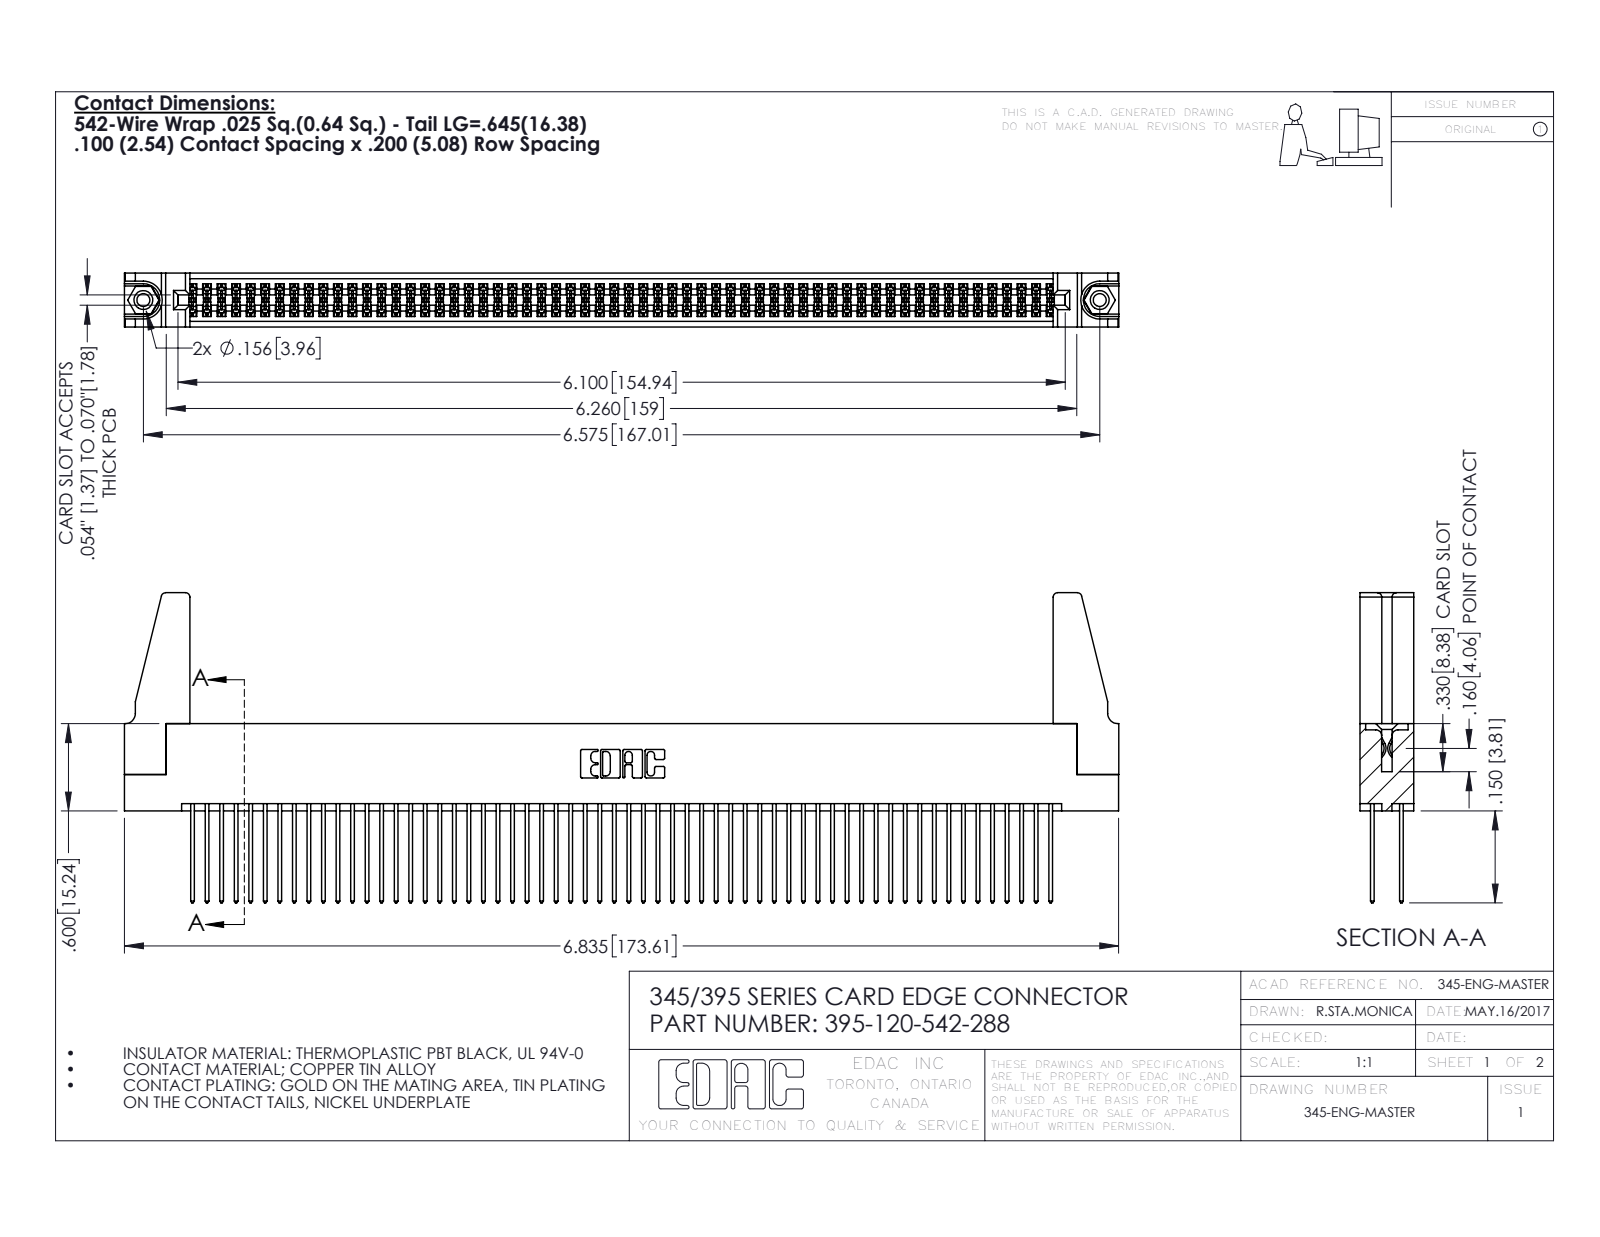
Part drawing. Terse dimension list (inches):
name: 345-292-001_345-293-142; 345 Part_Flush Mounting Lugs - 0.156 Dia-TH; 345-250-001_345-250-001-102; 345-220-078_345-220-088 (+1 more)
written by: SolidWorks 2016 (CONFIG_CONTROL_DESIGN)
unit: in
bodies: 125 solids, 6250 faces (4112 planar, 2122 cylindrical, 16 other)
size: 6.836 × 2.132 × 0.37
volume: 1.272 in³; area: 49.74 in²
holes: 2× ⌀0.089, 2× ⌀0.125, 2× ⌀0.156, 1× ⌀0.064
bosses: 2× ⌀0.155
rounds: 180× R0.006, 120× R0.01, 22× R0.01, 8× R0.03, 6× R0.007, 6× R0.031, 3× R0.026, 2× R0.014
face distances: 0.072, 0.298, 0.2, 0.098, 0.272, 0.025, 0.37, 0.225, 0.175, 0.149
hole spacings: 0.27, 6.339, 6.575
